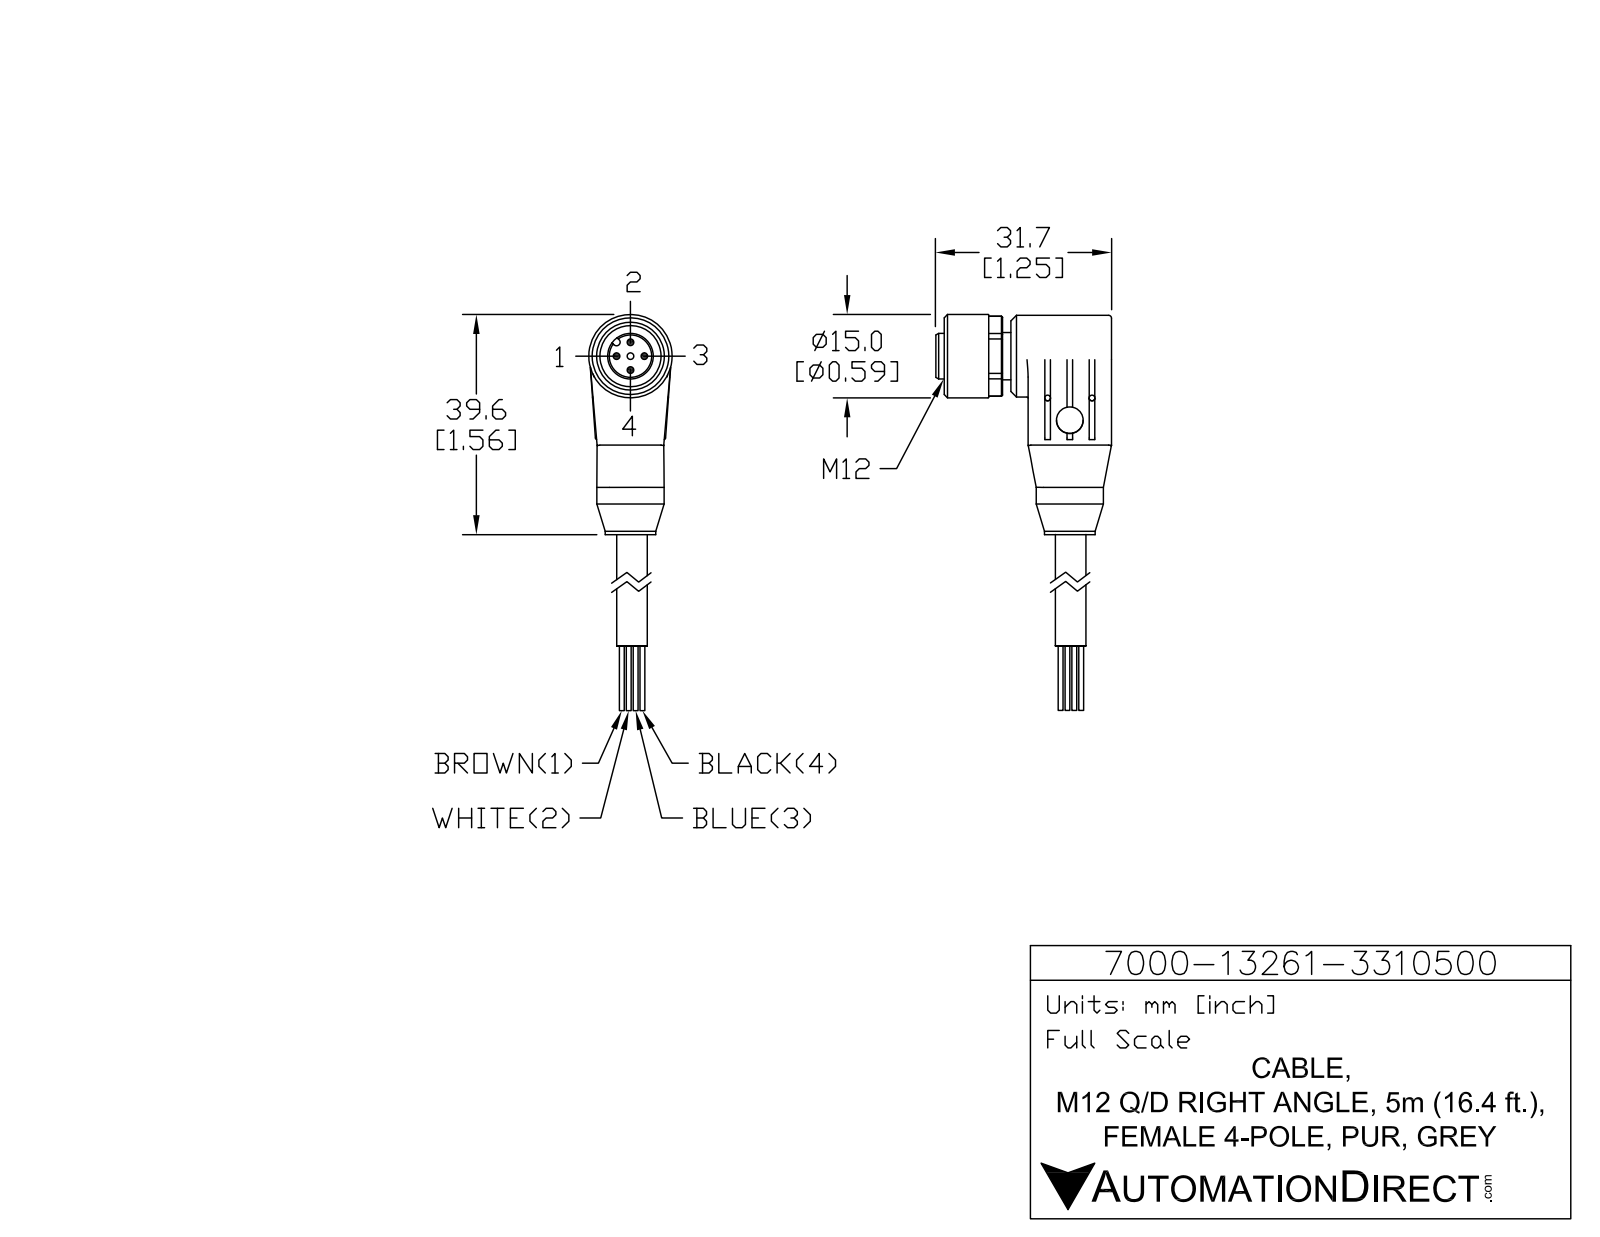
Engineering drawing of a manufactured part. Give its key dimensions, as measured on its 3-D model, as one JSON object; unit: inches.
{"part_name": "7000-13261-3310500", "step_written_by": "SolidWorks 2015 (AUTOMOTIVE_DESIGN)", "units": "inches", "bodies": {"solids": 1, "faces": 165, "planar": 70, "cylindrical": 61, "other": 34}, "overall_size": [2.346, 1.244, 0.591], "volume_in3": 0.558, "surface_area_in2": 6.25, "round_holes": [[0.047, 5], [0.041, 4], [0.189, 1], [0.433, 1]], "round_bosses_or_shafts": [[0.591, 1], [0.579, 1], [0.476, 1], [0.358, 1], [0.335, 1], [0.323, 1], [0.256, 1]], "partial_cylinders_radius": [[0.02, 4], [0.012, 2], [0.026, 1], [0.283, 1]], "face_to_face_distances": [0.591, 0.059, 0.772, 0.181, 0.472, 0.713, 0.122, 0.118, 0.299, 0.654], "hole_center_spacings": [0.098, 0.139, 0.197, 0.315]}
